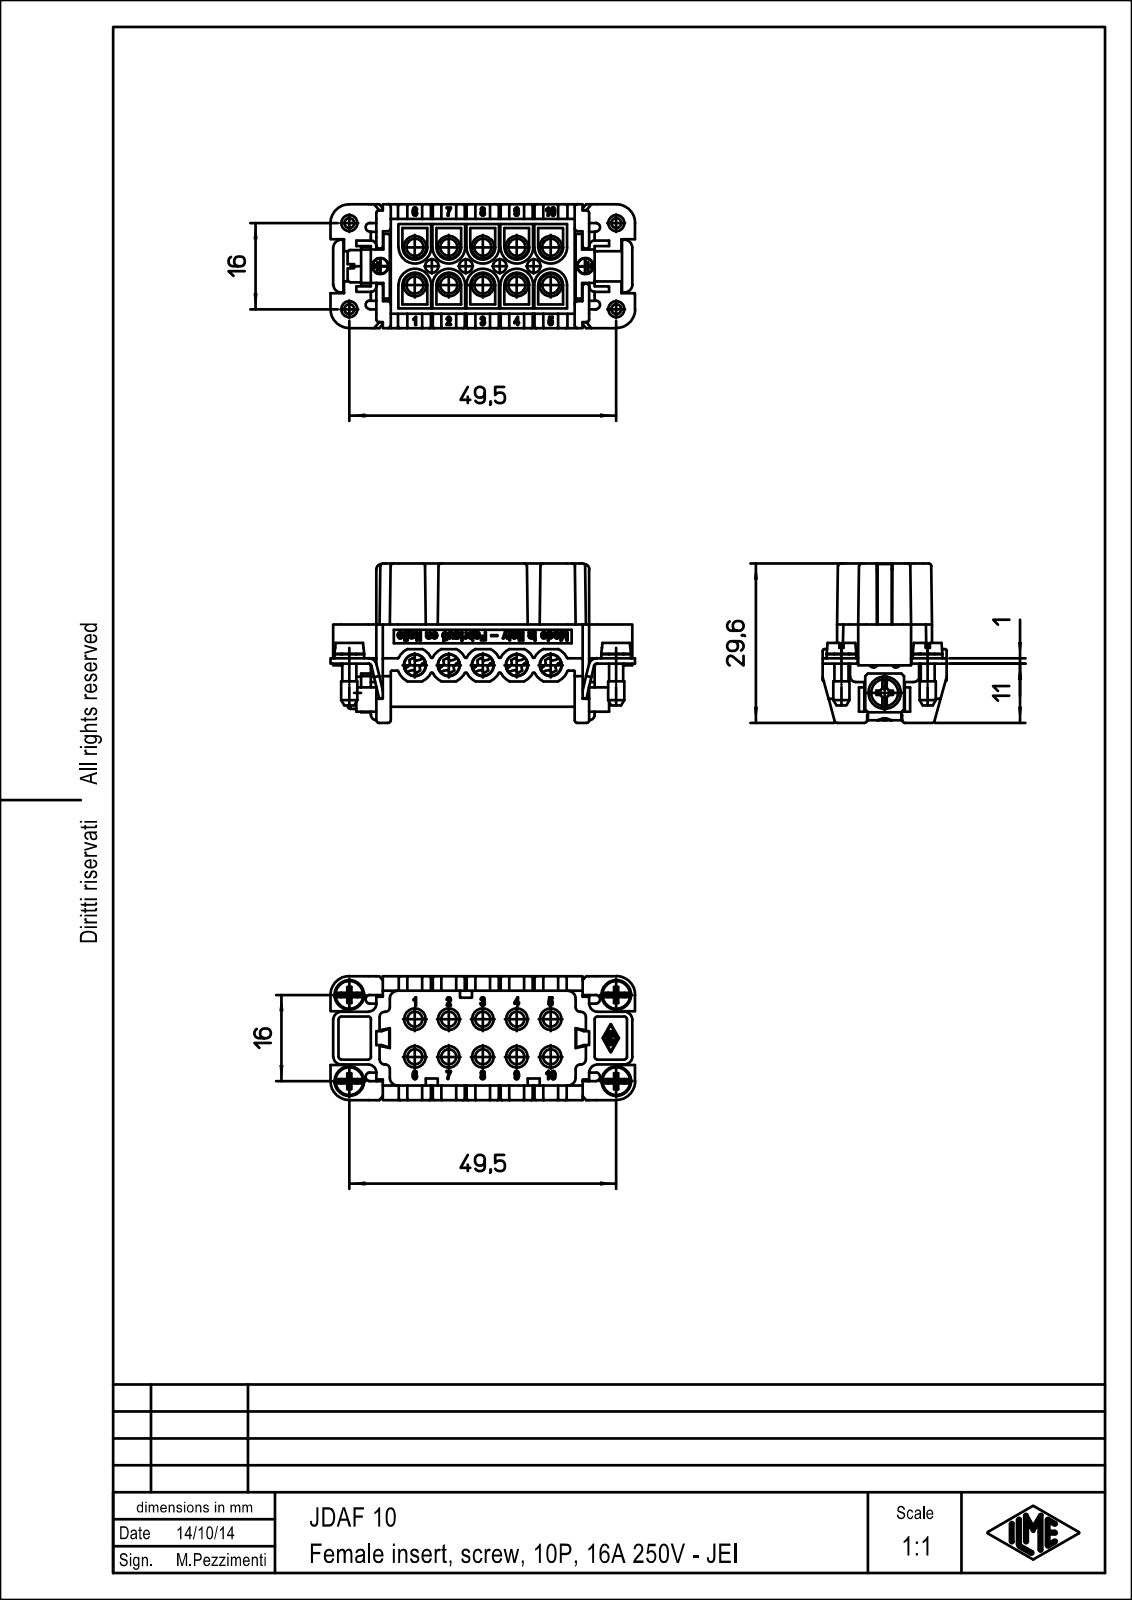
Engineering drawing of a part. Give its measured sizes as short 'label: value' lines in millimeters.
name: JDAF_10
written by: PTC Creo Elements/Direct Modeling 19.0B 21-Mar-2015 (C) Parametric Technology GmbH (AUTOMOTIVE_DESIGN)
unit: mm
bodies: 1 solid, 1374 faces (742 planar, 393 cylindrical, 239 other)
size: 56.5 × 29.6 × 23
volume: 17 926 mm³; area: 11 487 mm²
holes: 10× ⌀2.8, 10× ⌀3.2, 5× ⌀4.1, 4× ⌀2.5, 4× ⌀3, 1× ⌀1.8, 1× ⌀3.5
bosses: 5× ⌀3, 4× ⌀5.5, 4× ⌀2.6, 1× ⌀6
rounds: 54× R0.5, 21× R0.3, 16× R1.5, 14× R0.2, 14× R1, 8× R0.8, 5× R3.3, 4× R3.5
face distances: 1, 17.6, 2.7, 12.55, 8, 20.3, 7.3, 2.5, 6.3, 1.3
hole spacings: 4.71, 6.3, 10.08, 12.6, 9.42, 16.13, 18.9, 14.41
